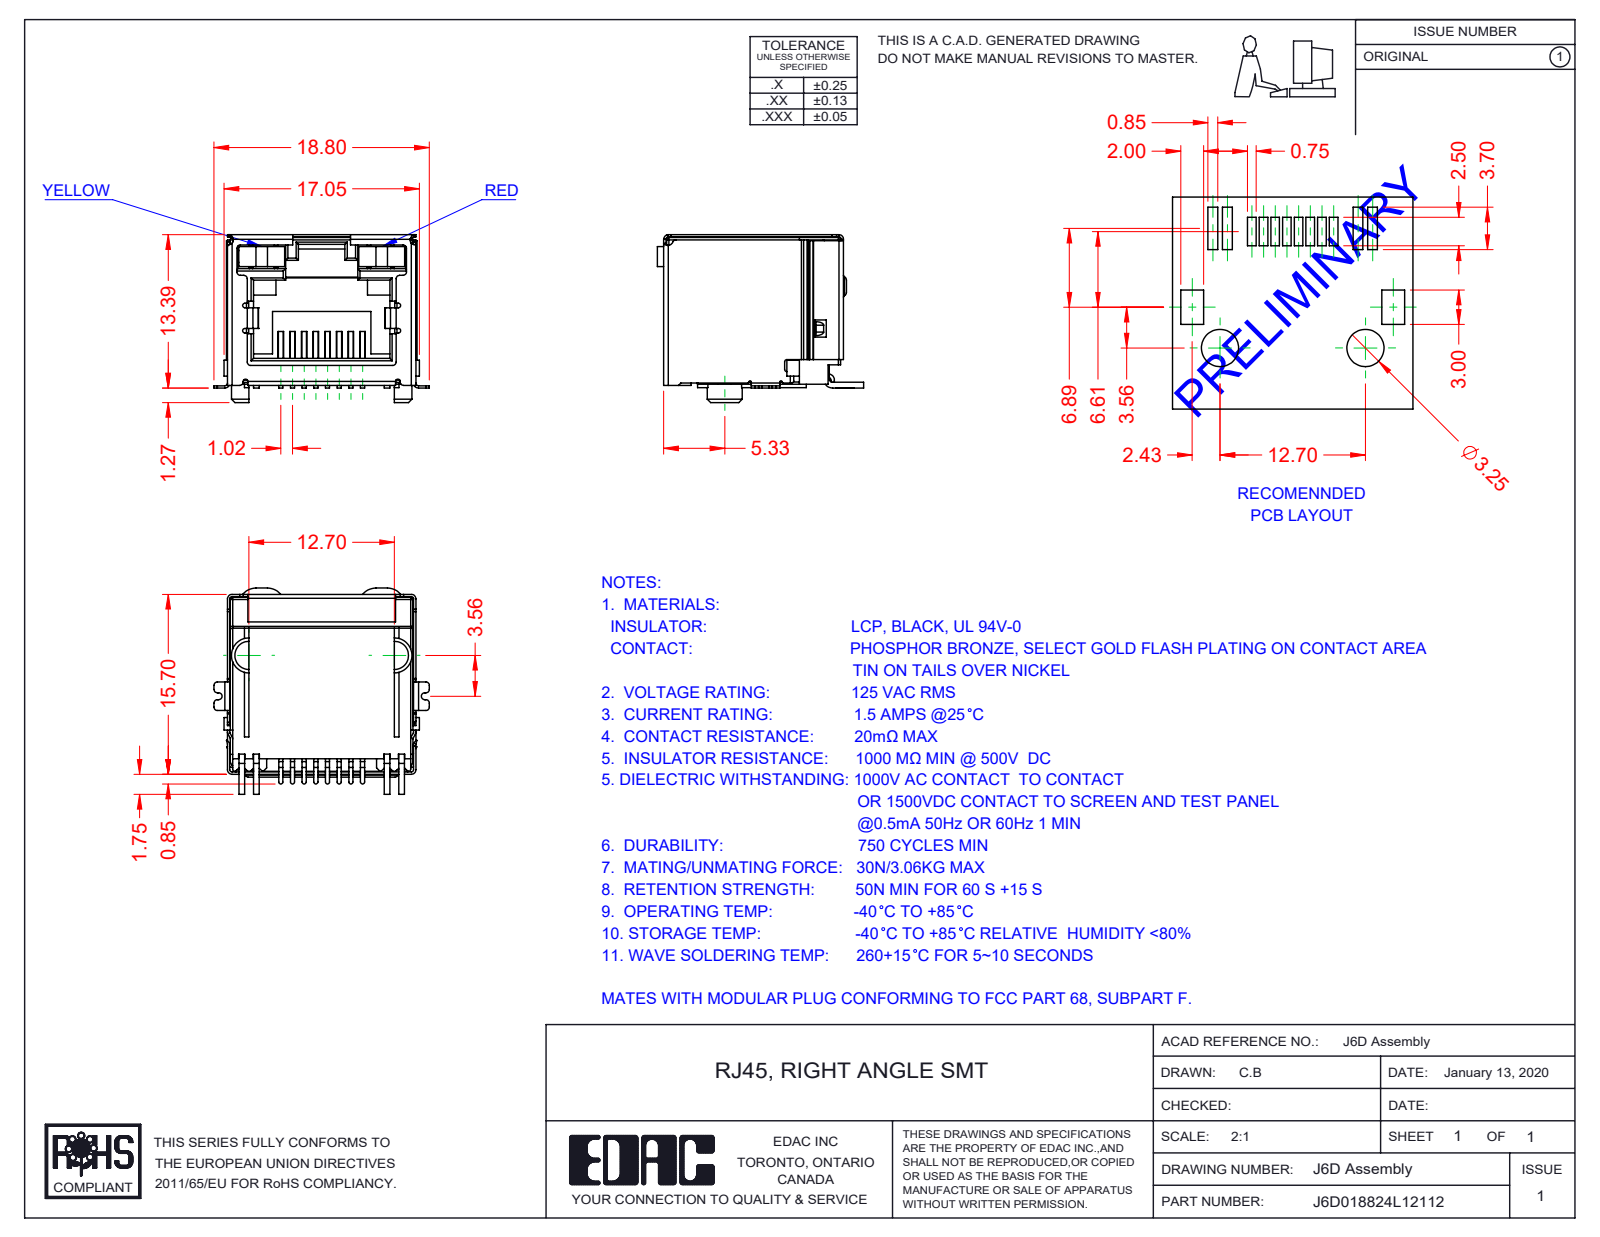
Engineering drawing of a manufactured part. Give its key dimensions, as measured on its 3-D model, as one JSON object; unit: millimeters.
{"part_name": "6D Shield_LED - No EMI; 6D Contacts; 6D Insulator; 6D LED LH_1-Yellow (+2 more)", "step_written_by": "SolidWorks 2016 (CONFIG_CONTROL_DESIGN)", "units": "millimeters", "bodies": {"solids": 12, "faces": 893, "planar": 644, "cylindrical": 216, "other": 33}, "overall_size": [18.8, 18, 14.65], "volume_mm3": 1804, "surface_area_mm2": 4898, "partial_cylinders_radius": [[0.3, 39], [0.2, 37], [0.4, 16], [0.1, 12], [0.15, 8], [0.18, 8], [0.5, 6], [1.5, 5]], "face_to_face_distances": [16, 16.25, 16.2, 2.25, 1, 15.95, 16.05, 12.8, 0.45, 16.45]}
